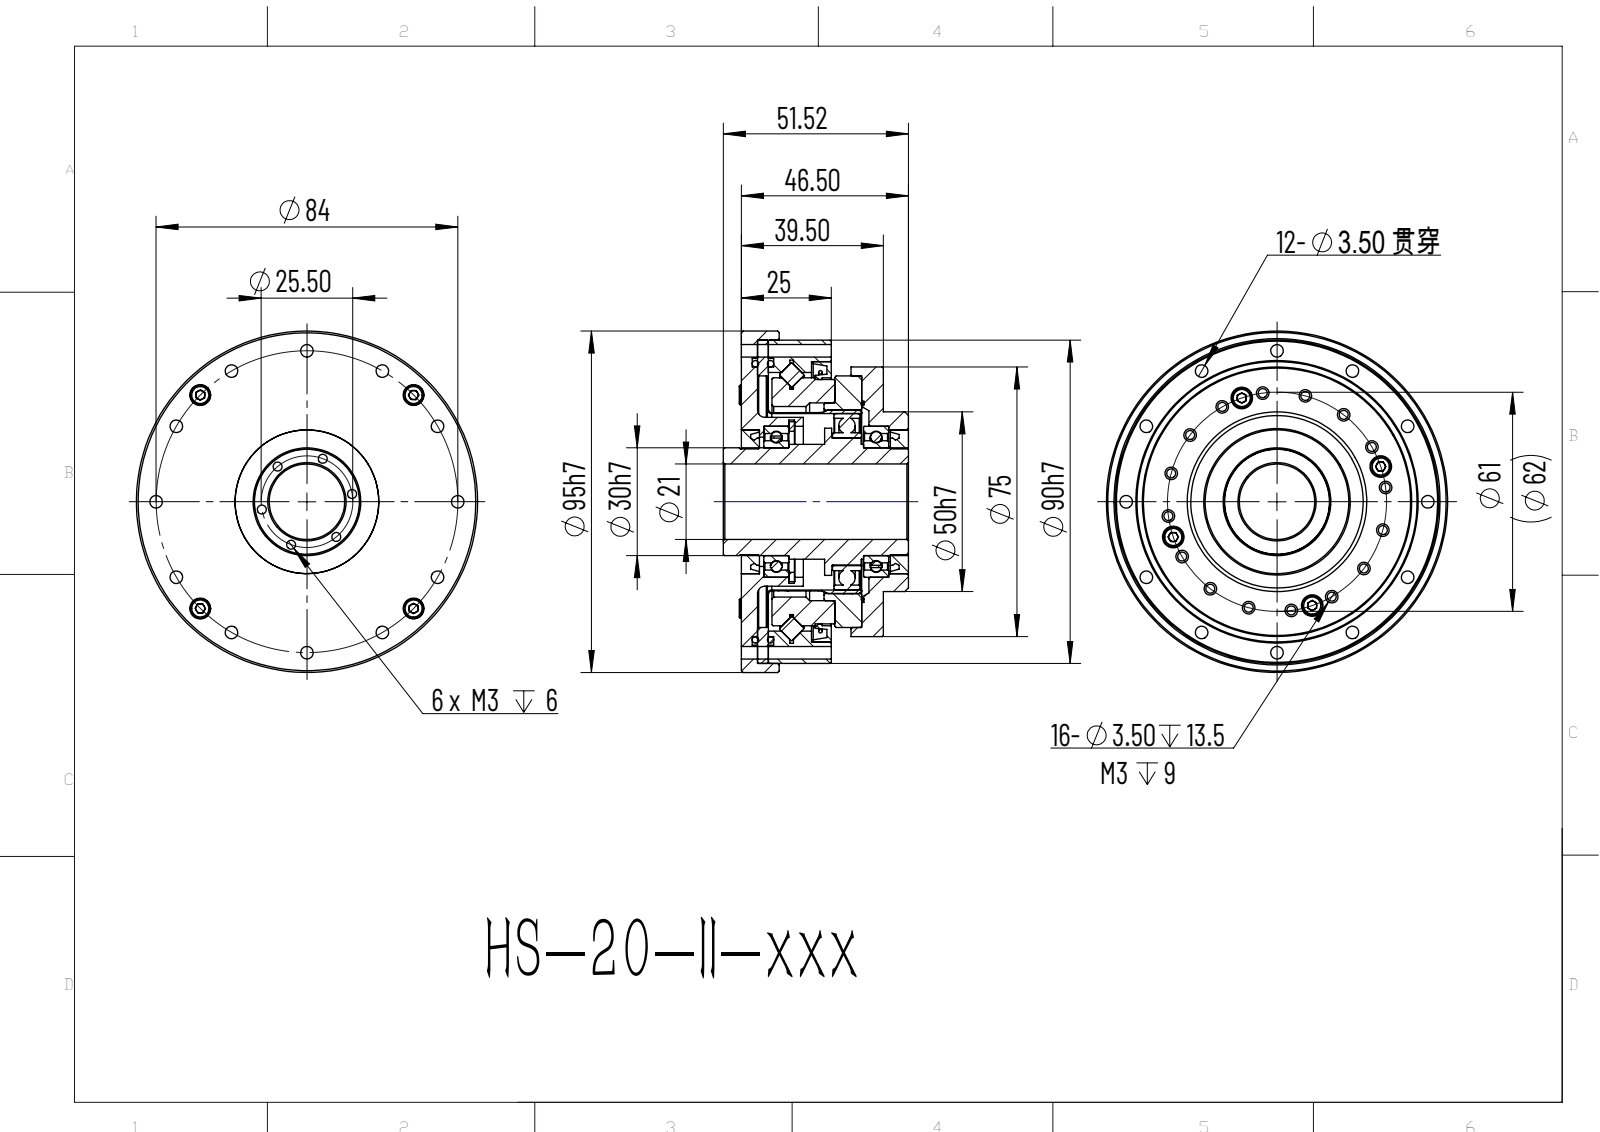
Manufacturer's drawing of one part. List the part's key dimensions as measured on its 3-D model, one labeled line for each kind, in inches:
Part name (STEP PRODUCT): HS-20-II; hexagon socket head cap screws gb_GB_FASTENER_SCREWS_HSHCS M3X8-S; ???40X30X5; O??????-??75X??18 (+8 more)
STEP written by: ONSHAPE BY PTC INC, 1.201 (AP242_MANAGED_MODEL_BASED_3D_ENGINEERING_MIM_LF)
Units: inches
Bodies: 97 solids, 1717 faces (591 planar, 514 cylindrical, 612 other)
Overall size (bounding box): 3.74 × 3.74 × 2.028
Volume: 10.53 in³ · Surface area: 204.5 in²
Round holes (diameter × count): ⌀0.138 ×32, ⌀0.098 ×30, ⌀0.134 ×8, ⌀0.139 ×8, ⌀0.236 ×8, ⌀0.081 ×1, ⌀0.114 ×1, ⌀0.197 ×1, ⌀0.827 ×1, ⌀1.4 ×1, ⌀1.417 ×1, ⌀1.575 ×1
Round bosses / shafts (diameter × count): ⌀0.197 ×36, ⌀0.217 ×8, ⌀0.118 ×8, ⌀3.74 ×1, ⌀3.543 ×1, ⌀2.953 ×1, ⌀2.717 ×1, ⌀2.472 ×1
Partial cylindrical surfaces — rounded edges, fillets, slot ends (radius × count): R0.099 ×36
Main face-to-face distances: 0.177, 0.295, 1.024, 0.118, 0.984, 0.846, 0.335, 0.689, 0.807, 0.039
Hole centre spacings: 1.654, 1.201, 0.856, 2.864, 3.194, 0.431, 1.266, 1.48
